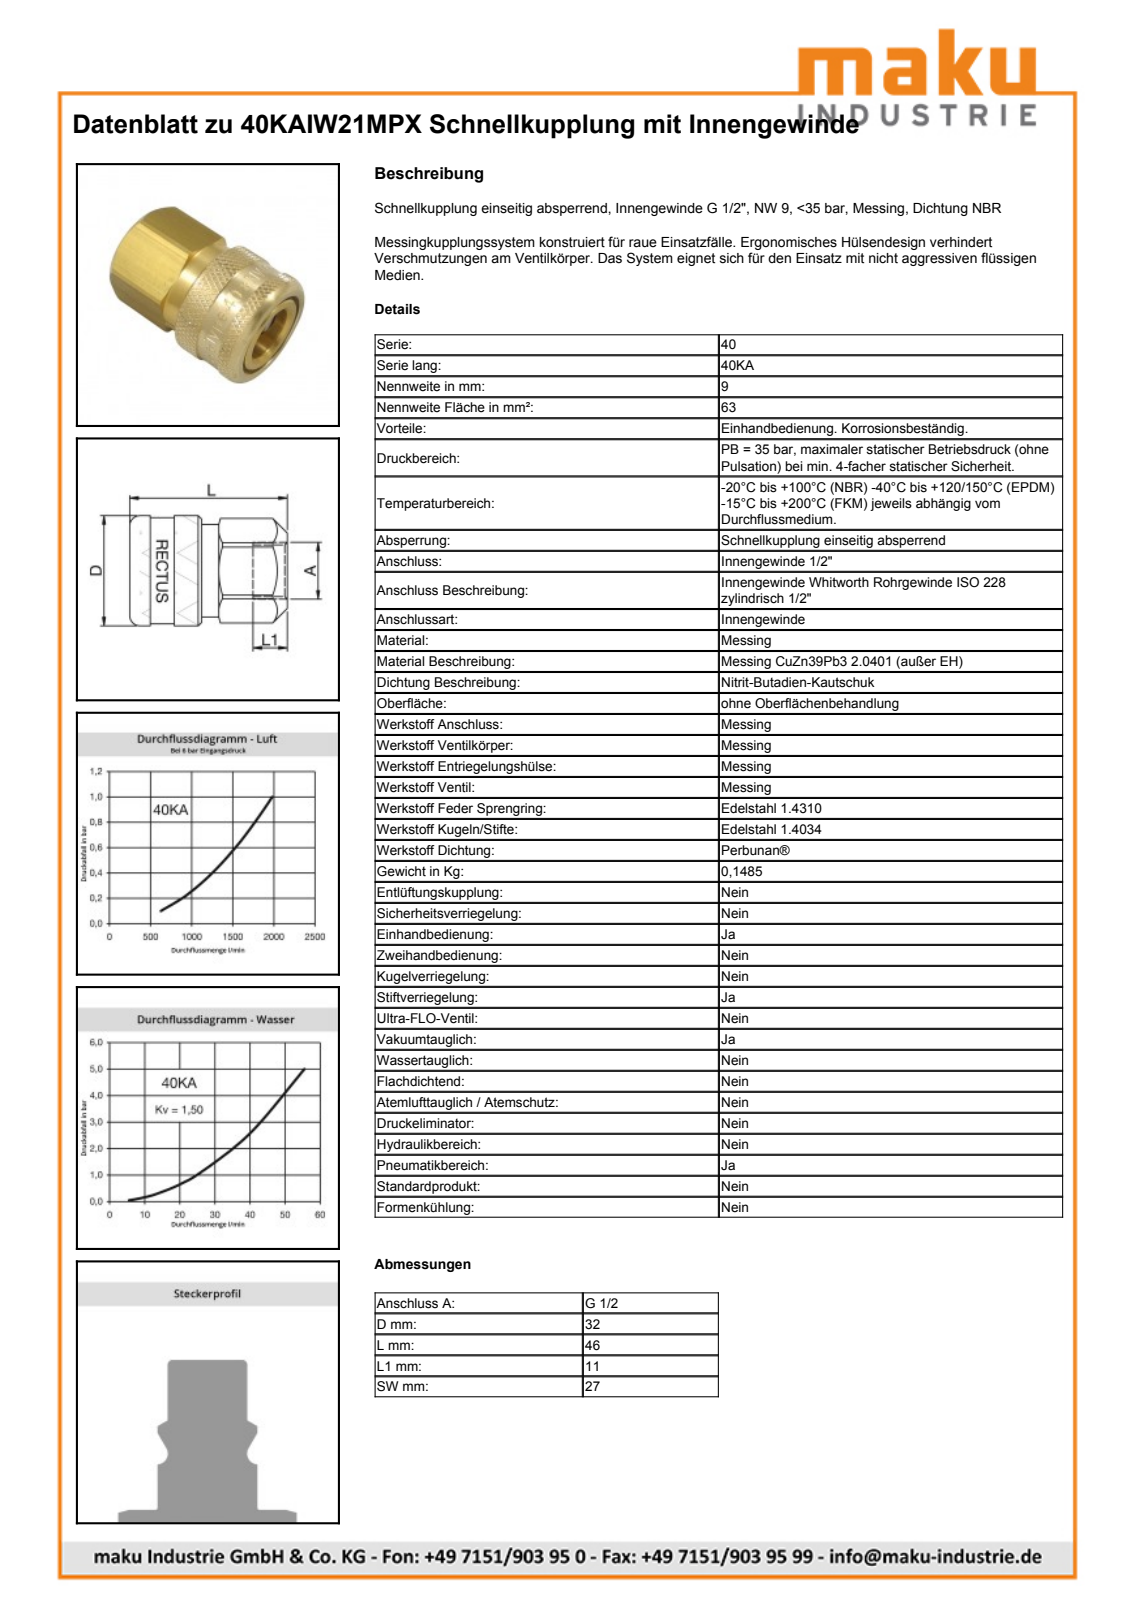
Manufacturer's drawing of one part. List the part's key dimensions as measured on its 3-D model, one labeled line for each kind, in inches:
Part name (STEP PRODUCT): D105842
STEP written by: Autodesk Inventor 2011 (AUTOMOTIVE_DESIGN)
Units: inches
Bodies: 2 solids, 591 faces (233 planar, 75 cylindrical, 283 other)
Overall size (bounding box): 1.811 × 1.266 × 1.266
Volume: 1.471 in³ · Surface area: 16.59 in²
Round holes (diameter × count): ⌀0.594 ×1, ⌀0.733 ×1, ⌀0.872 ×1, ⌀0.949 ×1, ⌀1.069 ×1, ⌀1.142 ×1
Round bosses / shafts (diameter × count): ⌀1.266 ×1, ⌀1.22 ×1, ⌀1.063 ×1, ⌀0.866 ×1, ⌀0.807 ×1
Partial cylindrical surfaces — rounded edges, fillets, slot ends (radius × count): R0.366 ×1, R0.411 ×1, R0.6 ×1, R0.606 ×1
Main face-to-face distances: 1.063, 1.378, 1.811, 0.433, 0.591, 0.787, 1.024, 0.549, 0.134, 0.695
